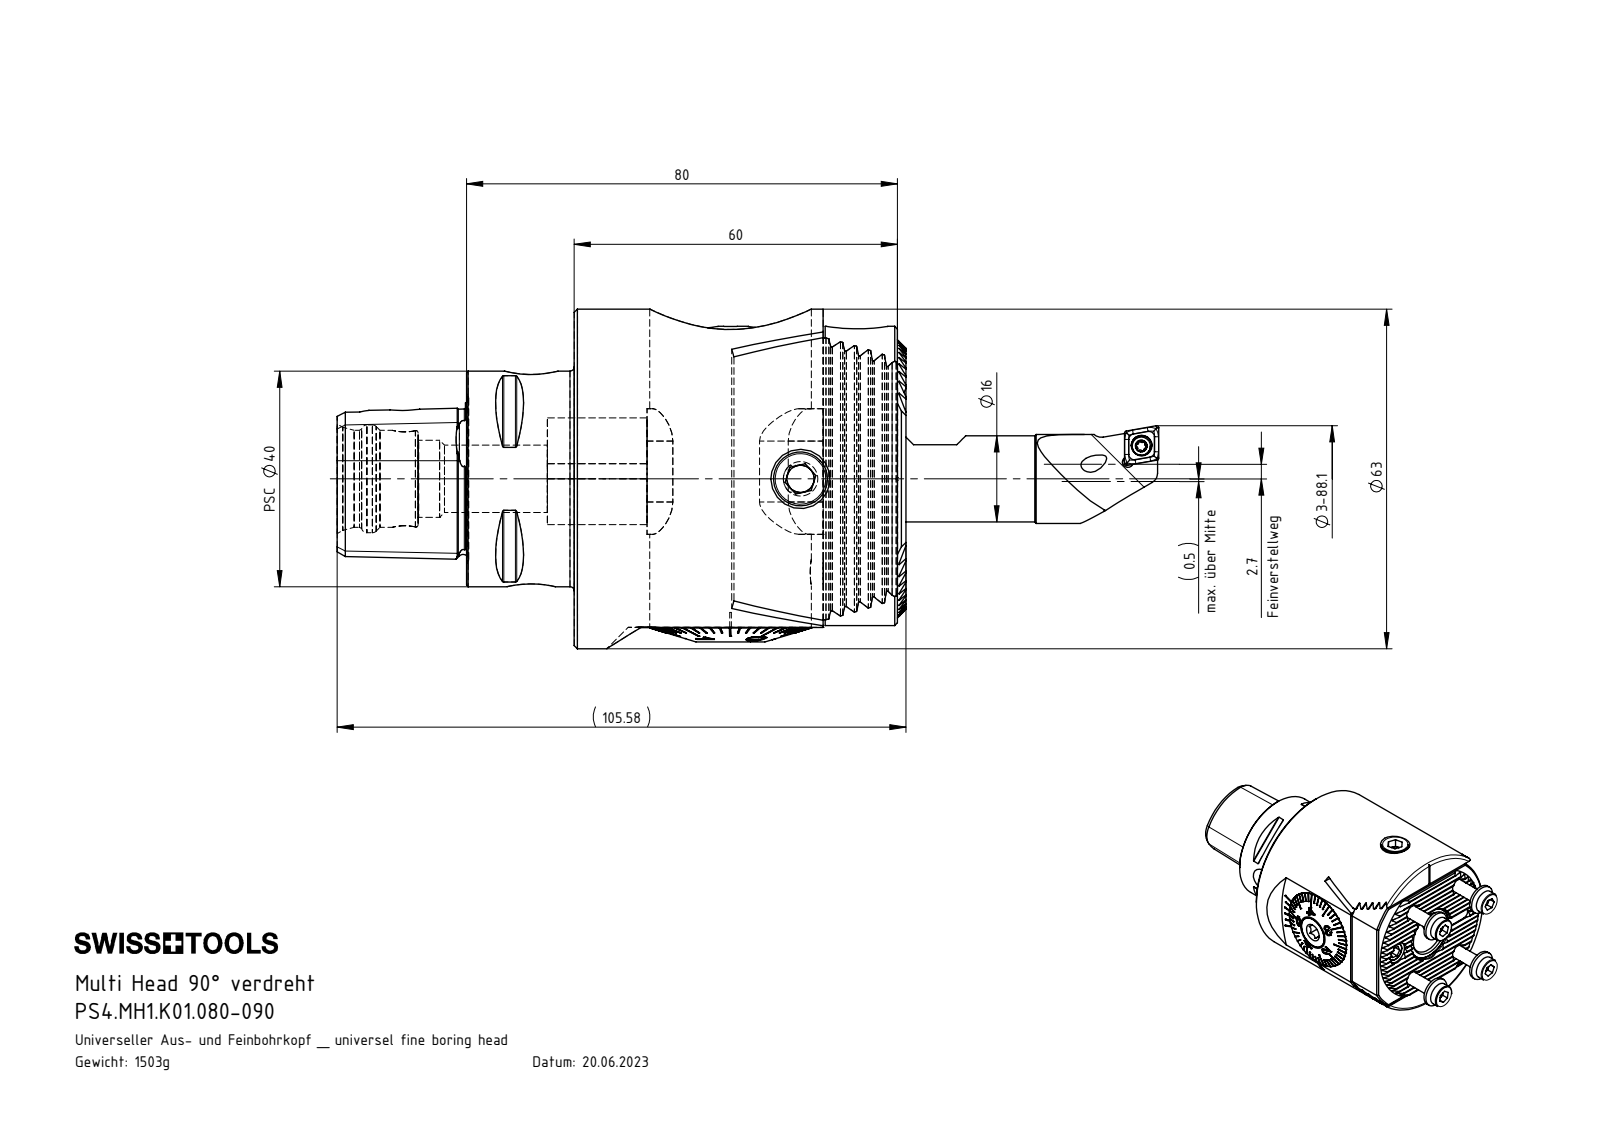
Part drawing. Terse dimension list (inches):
name: ISO 4026 - M8 x 6; MH1-BG1.001.049; A55-BG2.013.005_C; ISO 4026 - M4 x 5 (+8 more)
written by: SolidWorks 2017 (AUTOMOTIVE_DESIGN)
unit: in
bodies: 19 solids, 1272 faces (604 planar, 273 cylindrical, 395 other)
size: 4.787 × 2.48 × 2.48
volume: 11.69 in³; area: 102.3 in²
holes: 5× ⌀0.165, 4× ⌀0.335, 3× ⌀0.268, 3× ⌀0.433, 2× ⌀0.197, 2× ⌀0.787, 1× ⌀0.039, 1× ⌀0.063, 1× ⌀0.13, 1× ⌀0.181, 1× ⌀0.252, 1× ⌀0.315
bosses: 4× ⌀0.433, 4× ⌀0.335, 4× ⌀0.197, 3× ⌀0.394, 1× ⌀2.48, 1× ⌀1.575, 1× ⌀1.181, 1× ⌀1.18
rounds: 21× R0.006, 20× R0.008, 8× R0.012, 6× R0.236, 3× R0.157, 2× R0.335, 2× R1.22, 1× R0.079
face distances: 0.094, 1.835, 1.819, 0.016, 0.068, 0.188, 0.187, 0.341, 0.281, 0.205
hole spacings: 0.659, 0.71, 0.808, 0.925, 0.945, 1.181, 1.37, 1.513
